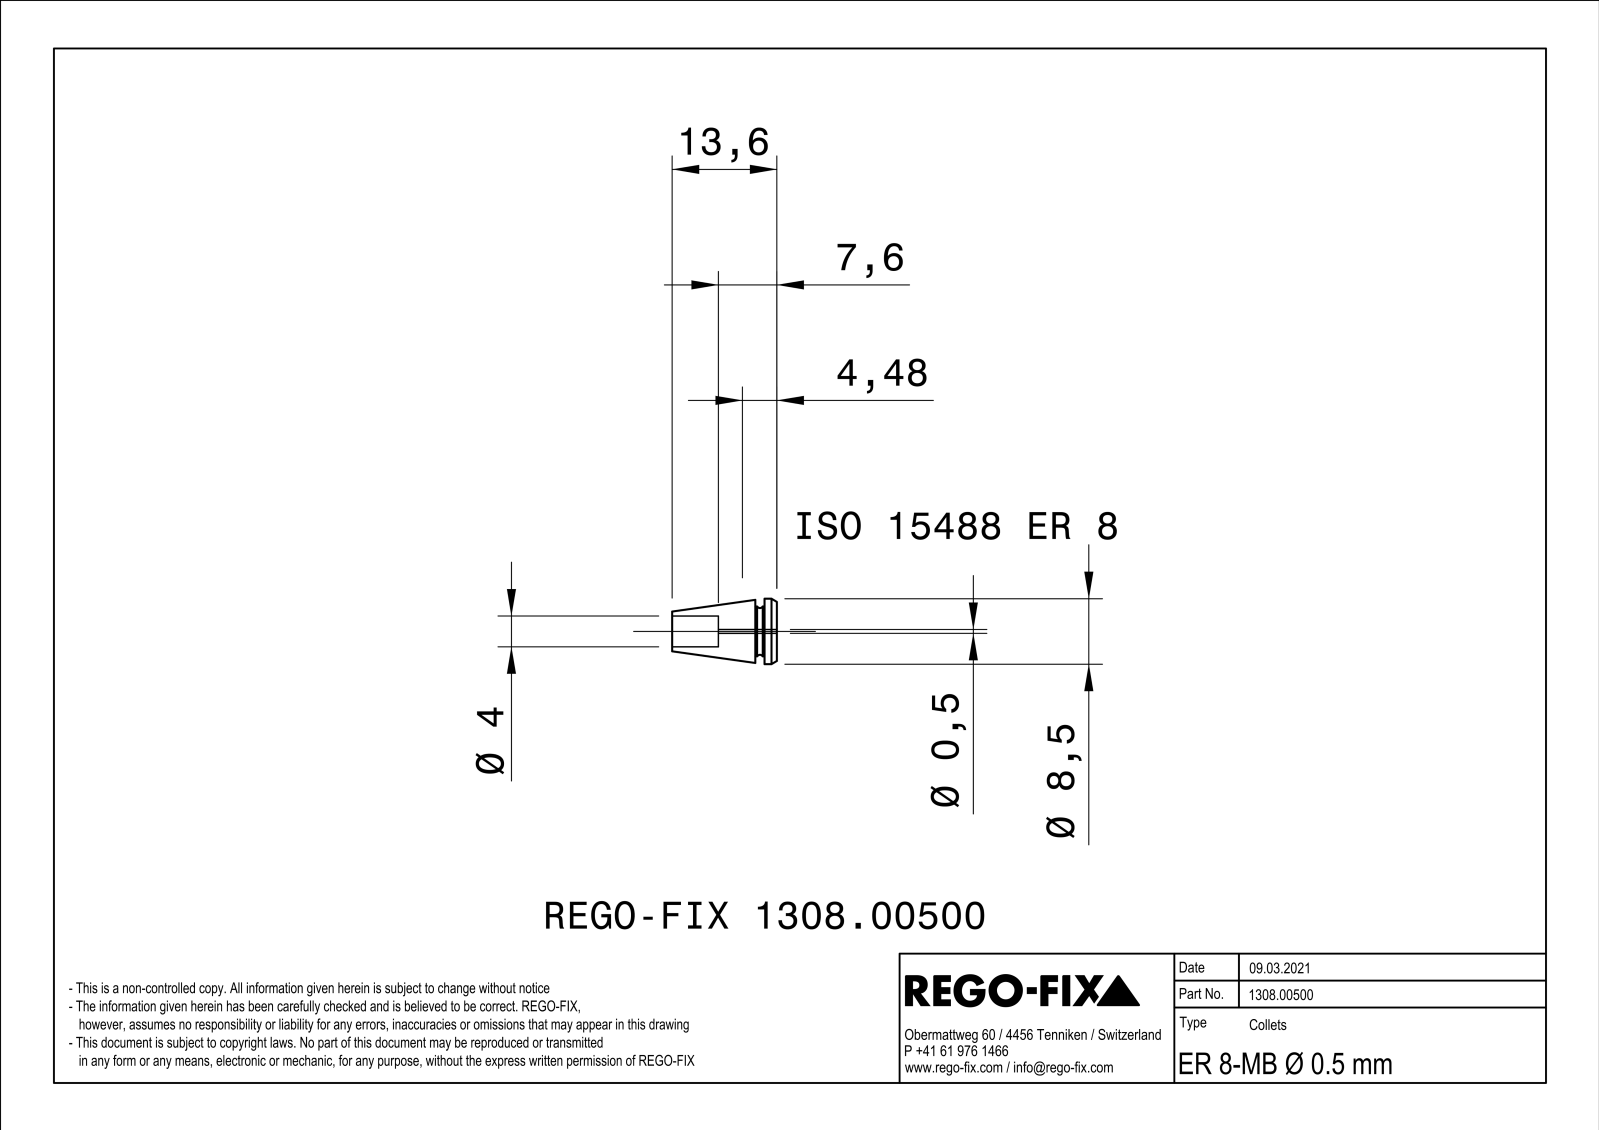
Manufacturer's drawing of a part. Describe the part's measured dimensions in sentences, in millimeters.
The part is named "NOCUT". Its 3-D file was written by "SIEMENS PLM Software Solid Edge ST10 (AUTOMOTIVE_DESIGN)". It is 1 solid with 83 faces: 27 planar, 25 cylindrical and 31 other. Overall it measures 13.6 by 8.5 by 8.49 millimeters. Its volume is 357 cubic millimeters and its surface area 721 square millimeters. Round holes: 3 of diameter 1.2, 1 of diameter 4. Round bosses or shafts: 1 of diameter 8.5, 1 of diameter 6.5. Partial cylindrical surfaces (rounded edges, fillets, slot ends): 3 of radius 25, 1 of radius 0.25. The main face-to-face distances are 0.6, 0.41, 1.6, 2.8, 1.2, 6, 7.6, 4.8, 11.2, 9.6. The hole center spacings are 1.35, 2.34.
